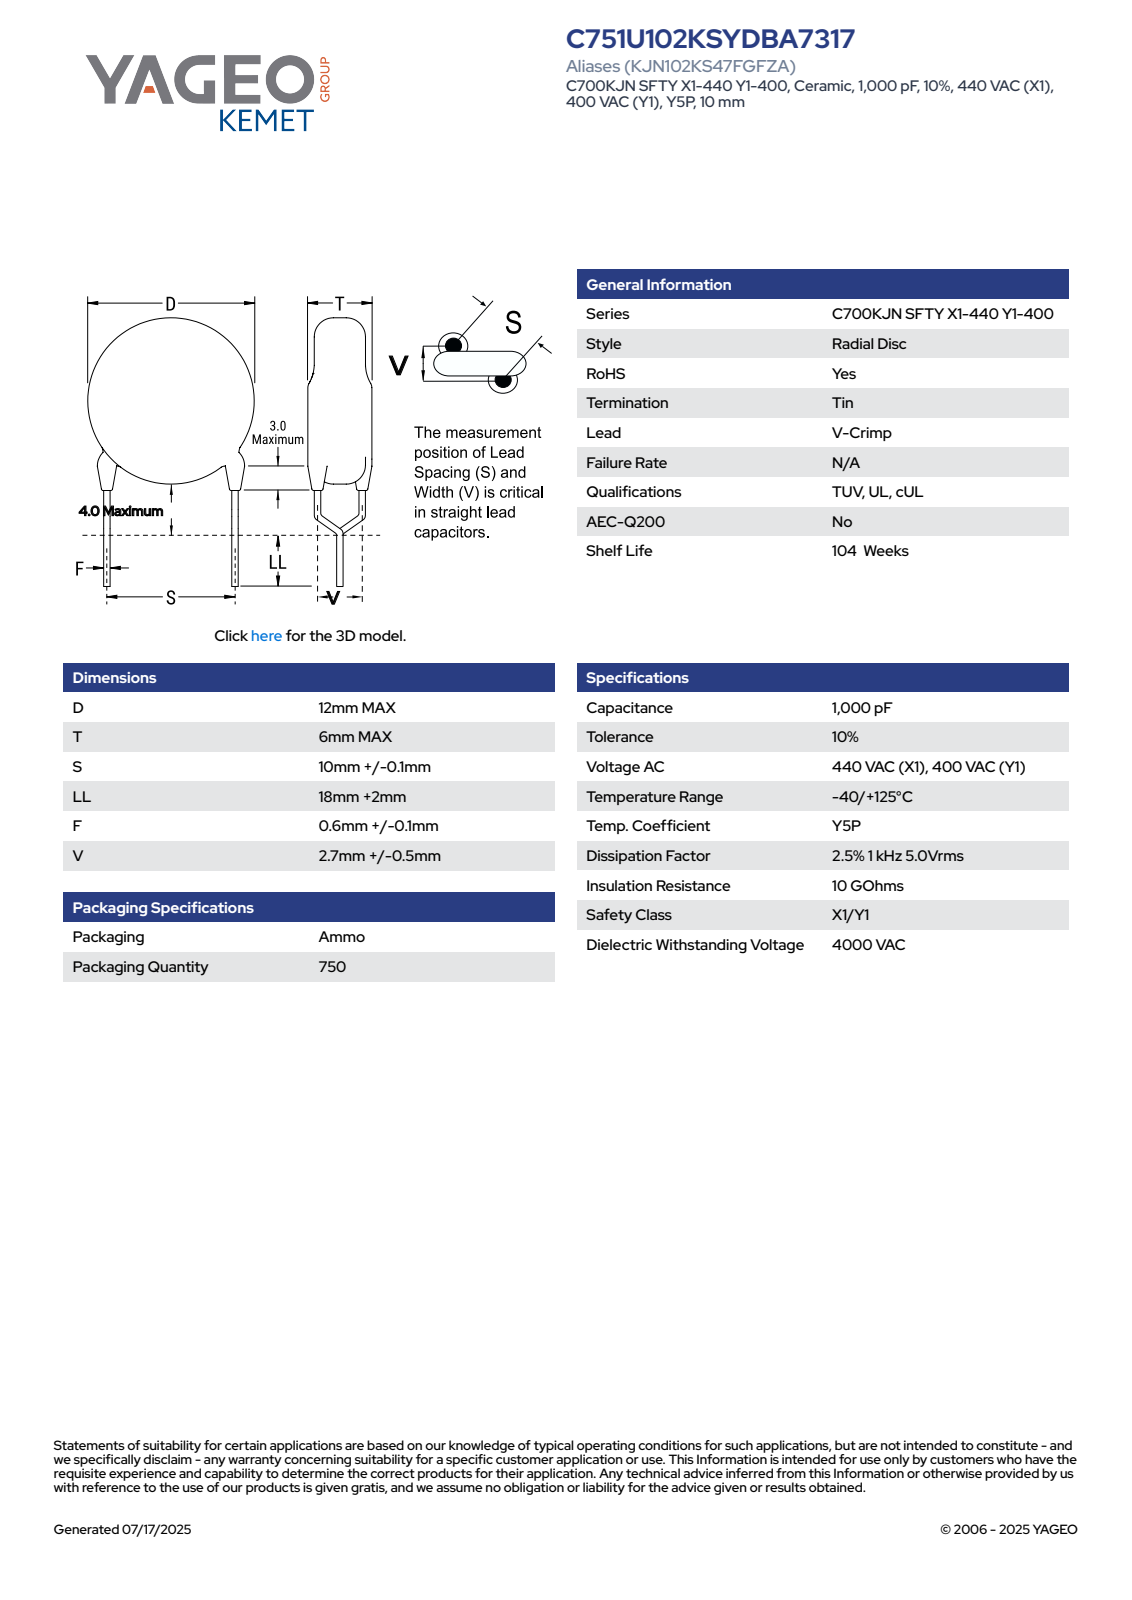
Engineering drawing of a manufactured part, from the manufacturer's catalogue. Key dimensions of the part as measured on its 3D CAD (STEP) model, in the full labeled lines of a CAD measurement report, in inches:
Part name (STEP PRODUCT): CCD_VC12X6_D12T6S10LL20F0.7V2.7
STEP written by: SolidWorks 2021 (AUTOMOTIVE_DESIGN)
Units: inches
Bodies: 4 solids, 88 faces (63 planar, 21 cylindrical, 4 other)
Overall size (bounding box): 1.26 × 0.479 × 0.236
Volume: 0.042 in³ · Surface area: 0.856 in²
Round bosses / shafts (diameter × count): ⌀0.028 ×6, ⌀0.047 ×2, ⌀0.472 ×1
Partial cylindrical surfaces — rounded edges, fillets, slot ends (radius × count): R0.024 ×2
Main face-to-face distances: 0.236, 0.787, 1.08, 0.293, 1.004, 0.217, 0.076, 0.021, 0.014, 0.312
